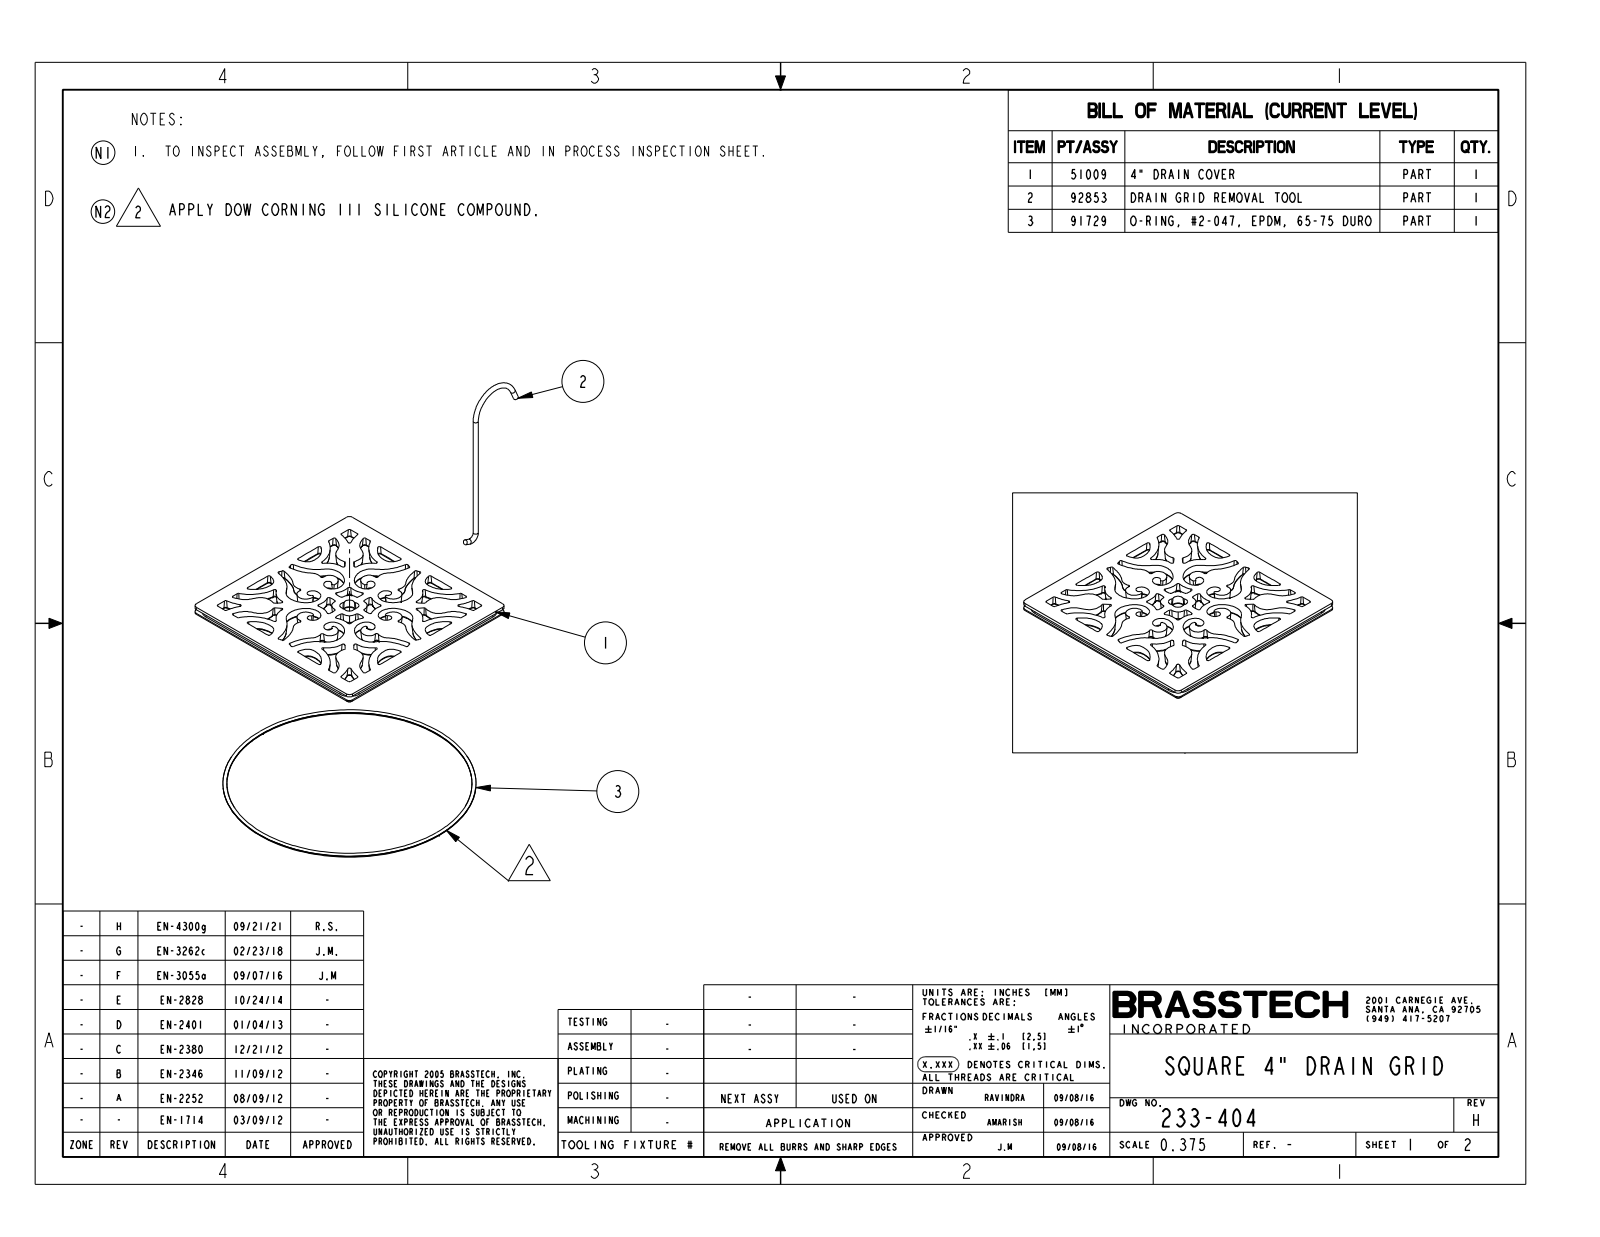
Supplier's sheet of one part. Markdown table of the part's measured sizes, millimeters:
| quantity | value |
| --- | --- |
| part name | 51009 |
| STEP written by | CREO PARAMETRIC BY PTC INC, 2018400 (AUTOMOTIVE_DESIGN) |
| units | millimeters |
| bodies | 1 solid, 556 faces (36 planar, 28 cylindrical, 492 other) |
| overall size | 102.7 × 102.7 × 4.8 |
| volume | 32 840 mm³ |
| surface area | 25 020 mm² |
| partial cylindrical surfaces (radius × count) | 0.8 × 12, 2 × 4, 6.4 × 4 |
| main face-to-face distances | 4.8, 1, 101.7, 1.4, 3.4, 3.4, 2, 1.4, 102.7, 100.6 |
